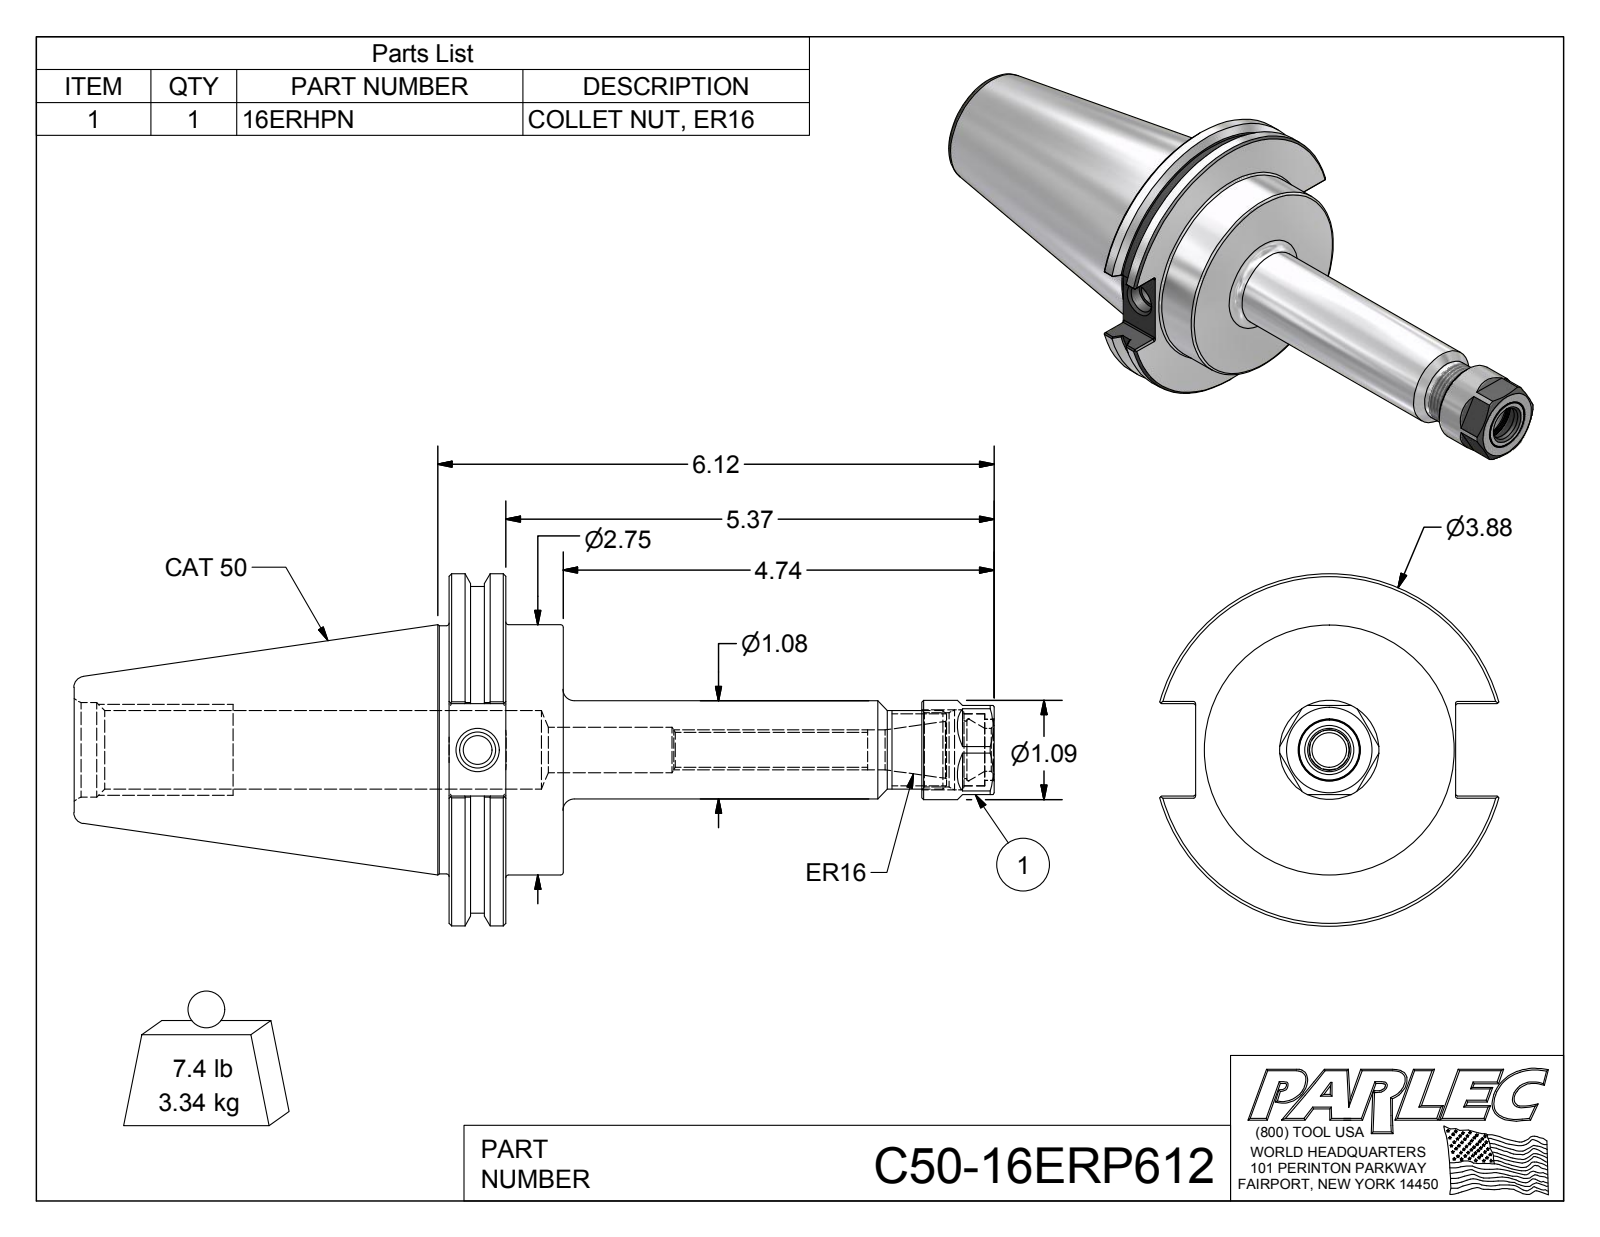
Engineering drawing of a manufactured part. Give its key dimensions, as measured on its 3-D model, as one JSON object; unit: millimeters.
{"part_name": "C50-16ERP612; C50-16ER6-1; 16ERHPN", "step_written_by": "Autodesk Inventor 2012 (AUTOMOTIVE_DESIGN)", "units": "millimeters", "bodies": {"solids": 3, "faces": 138, "planar": 53, "cylindrical": 39, "other": 46}, "overall_size": [257, 98.4, 94.7], "volume_mm3": 428700, "surface_area_mm2": 65940, "round_holes": [[8, 1], [9.7, 1], [10.1, 1], [11.2, 1], [12, 1], [12.7, 1], [16, 1], [17.1, 1], [17.3, 1], [20.2, 1], [20.7, 1], [22, 1]], "round_bosses_or_shafts": [[98.4, 1], [91.3, 1], [69.9, 1], [69.3, 1], [27.7, 1], [27.4, 1], [22, 1], [20.1, 1]], "partial_cylinders_radius": [[0.5, 12]], "face_to_face_distances": [31.9, 15.9, 16, 104.8, 120.7, 136.7, 24.9, 257, 152.3, 136.4]}
